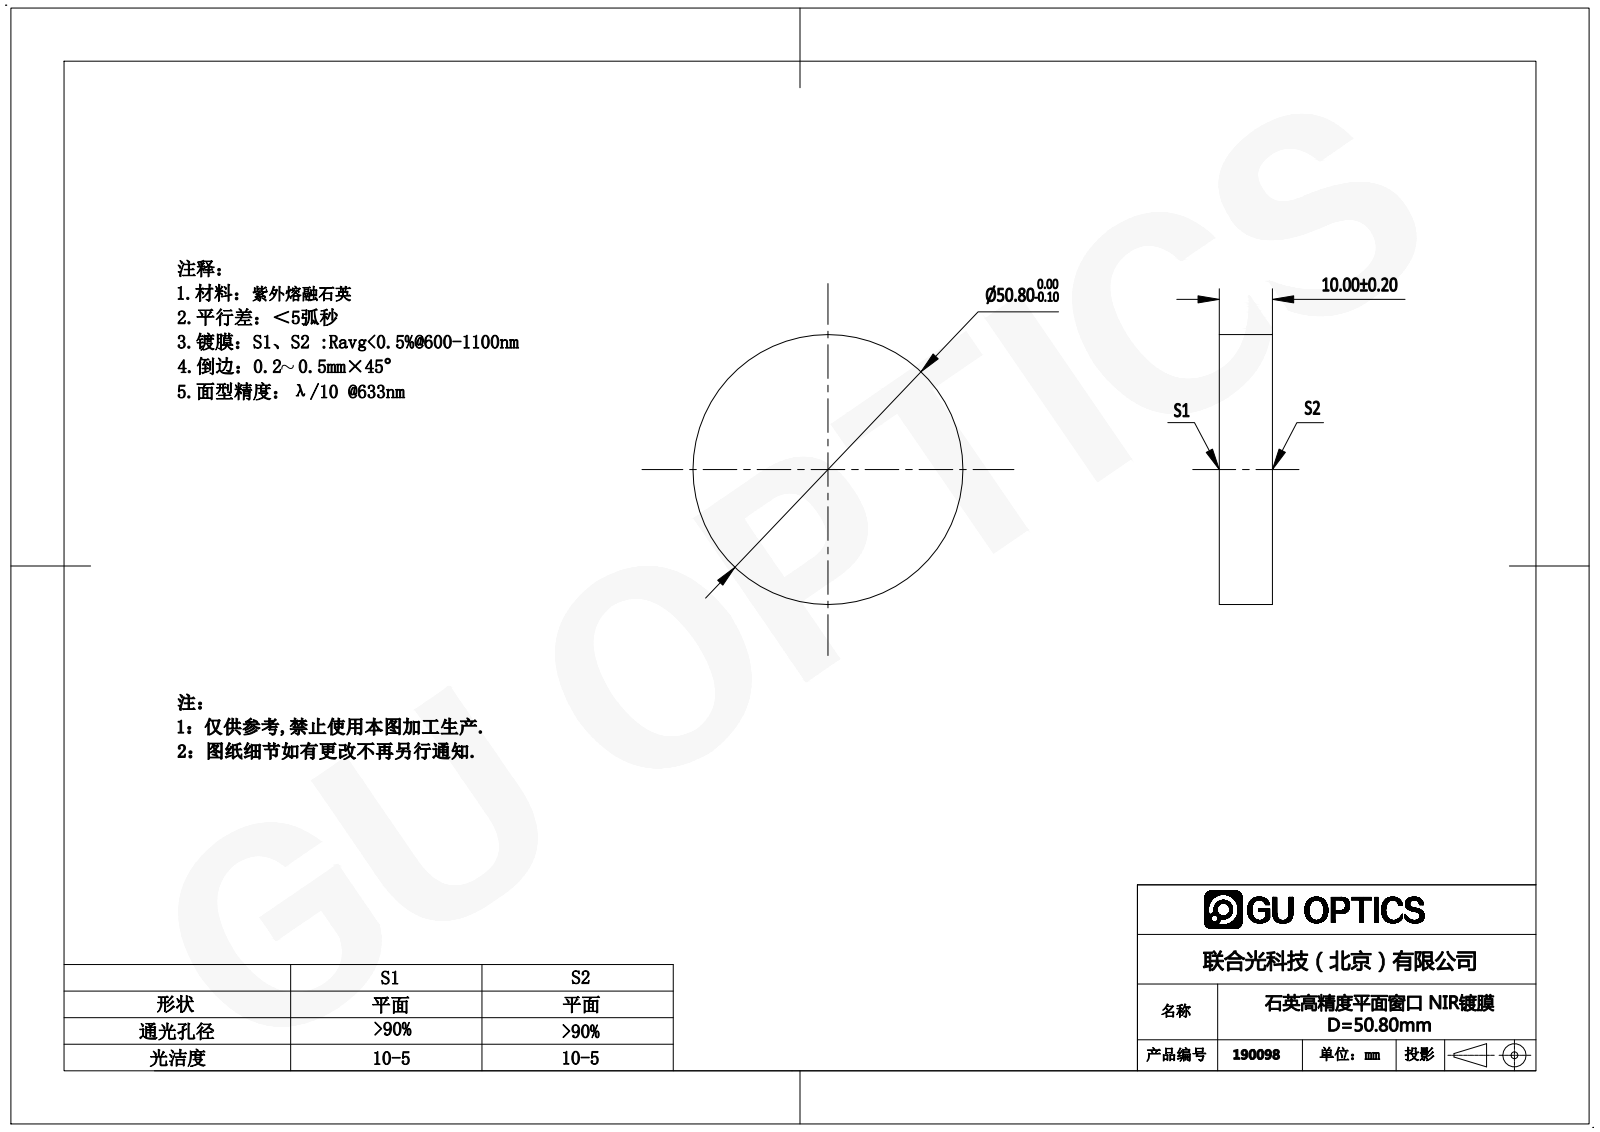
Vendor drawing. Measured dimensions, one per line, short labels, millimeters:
name: 190065
written by: SolidWorks 2016 (AUTOMOTIVE_DESIGN)
unit: mm
bodies: 1 solid, 4 faces (2 planar, 2 cylindrical, 0 other)
size: 50.8 × 50.8 × 10
volume: 20 268 mm³; area: 5 650 mm²
bosses: 1× ⌀50.8
face distances: 10
